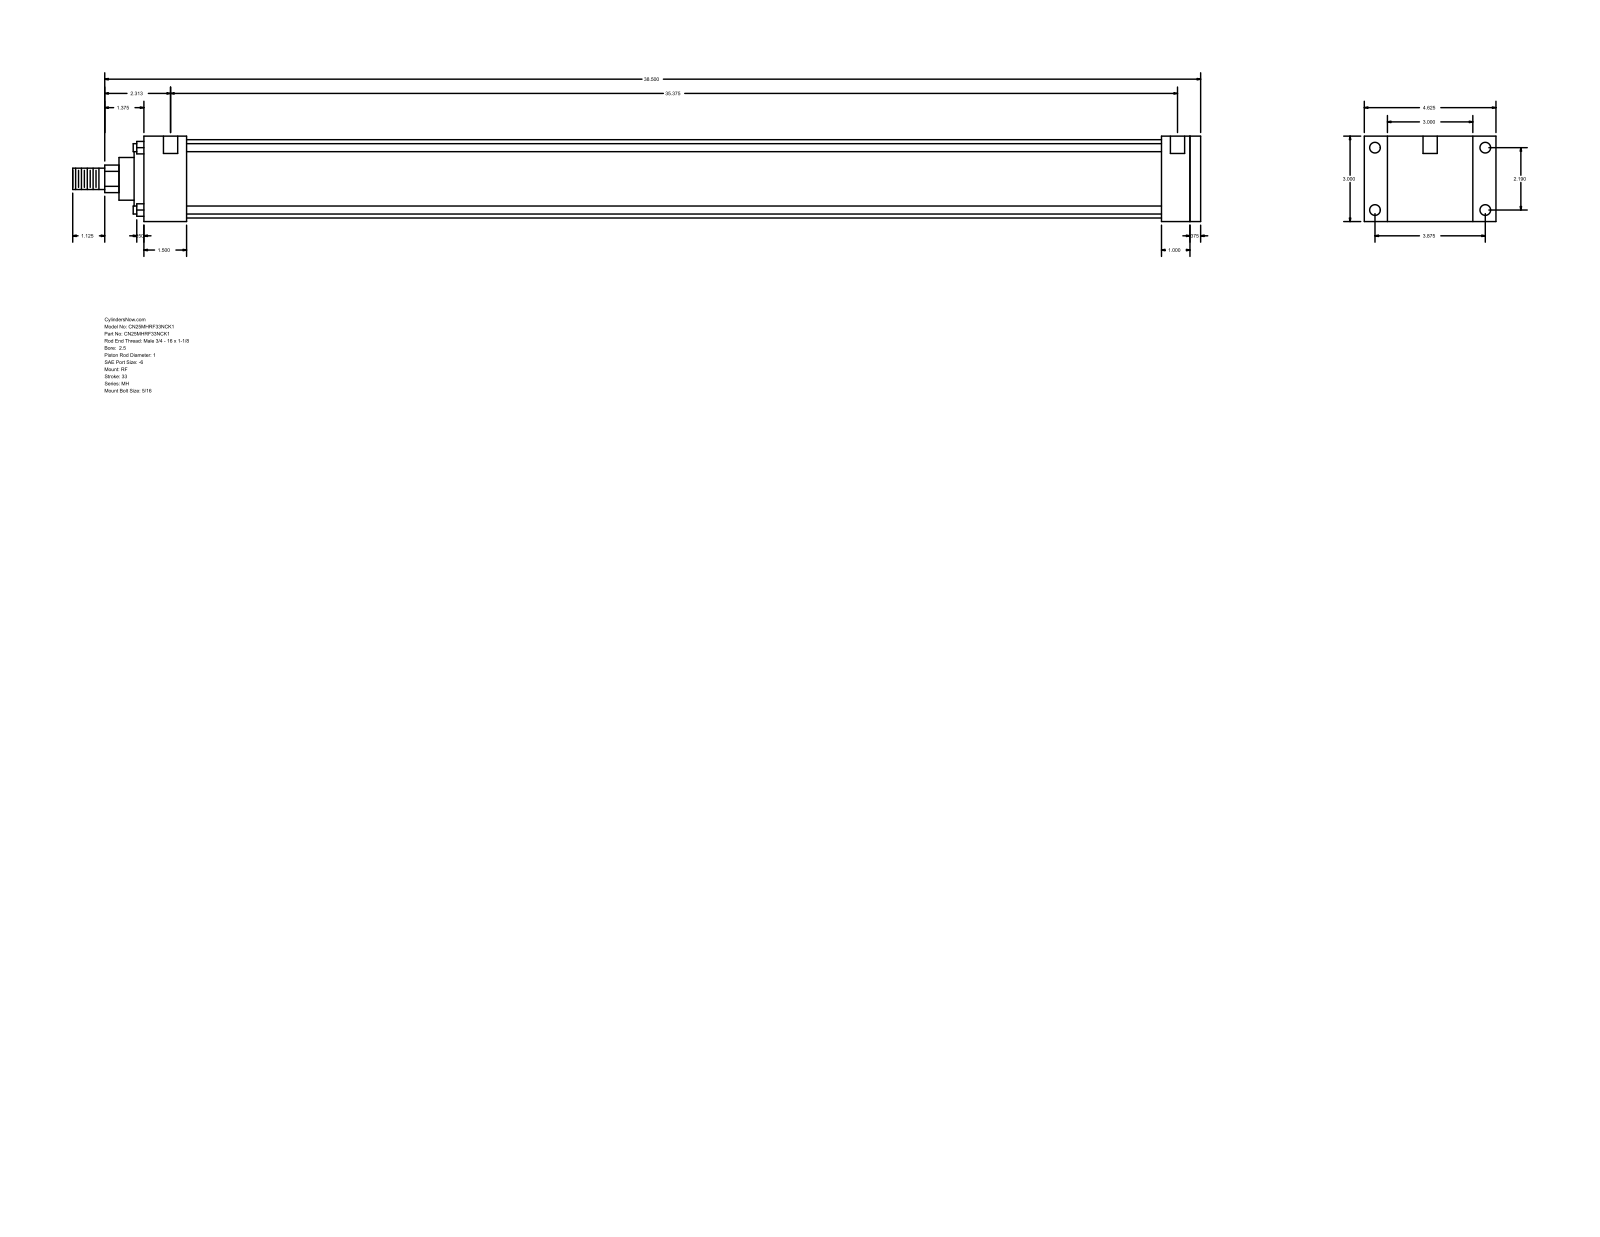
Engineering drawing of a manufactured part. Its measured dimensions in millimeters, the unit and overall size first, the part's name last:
Units: millimetres
Overall size (bounding box): 1006.48 × 117.47 × 76.2
Round holes (diameter × count): ⌀5.56 ×4, ⌀9.53 ×4, ⌀12.7 ×2
Round bosses / shafts (diameter × count): ⌀7.14 ×4, ⌀69.85 ×1, ⌀60.33 ×1, ⌀38.1 ×1, ⌀25.4 ×1, ⌀19.05 ×1
Partial cylindrical surfaces — rounded edges, fillets, slot ends (radius × count): R12.29 ×1
Main face-to-face distances: 76.2, 9.52, 942.98, 933.46, 25.4, 34.92, 908.06, 38.11, 869.95, 895.35
Hole centre spacings: 55.62, 98.42, 113.05, 906.46, 3.18, 4.76, 898.52, 901.7
Bodies: 0 solids, 94 faces (65 planar, 29 cylindrical, 0 other)
Part name (STEP PRODUCT): MH_RF__0250_1
STEP written by: GSSL Pune (CONFIG_CONTROL_DESIGN)
